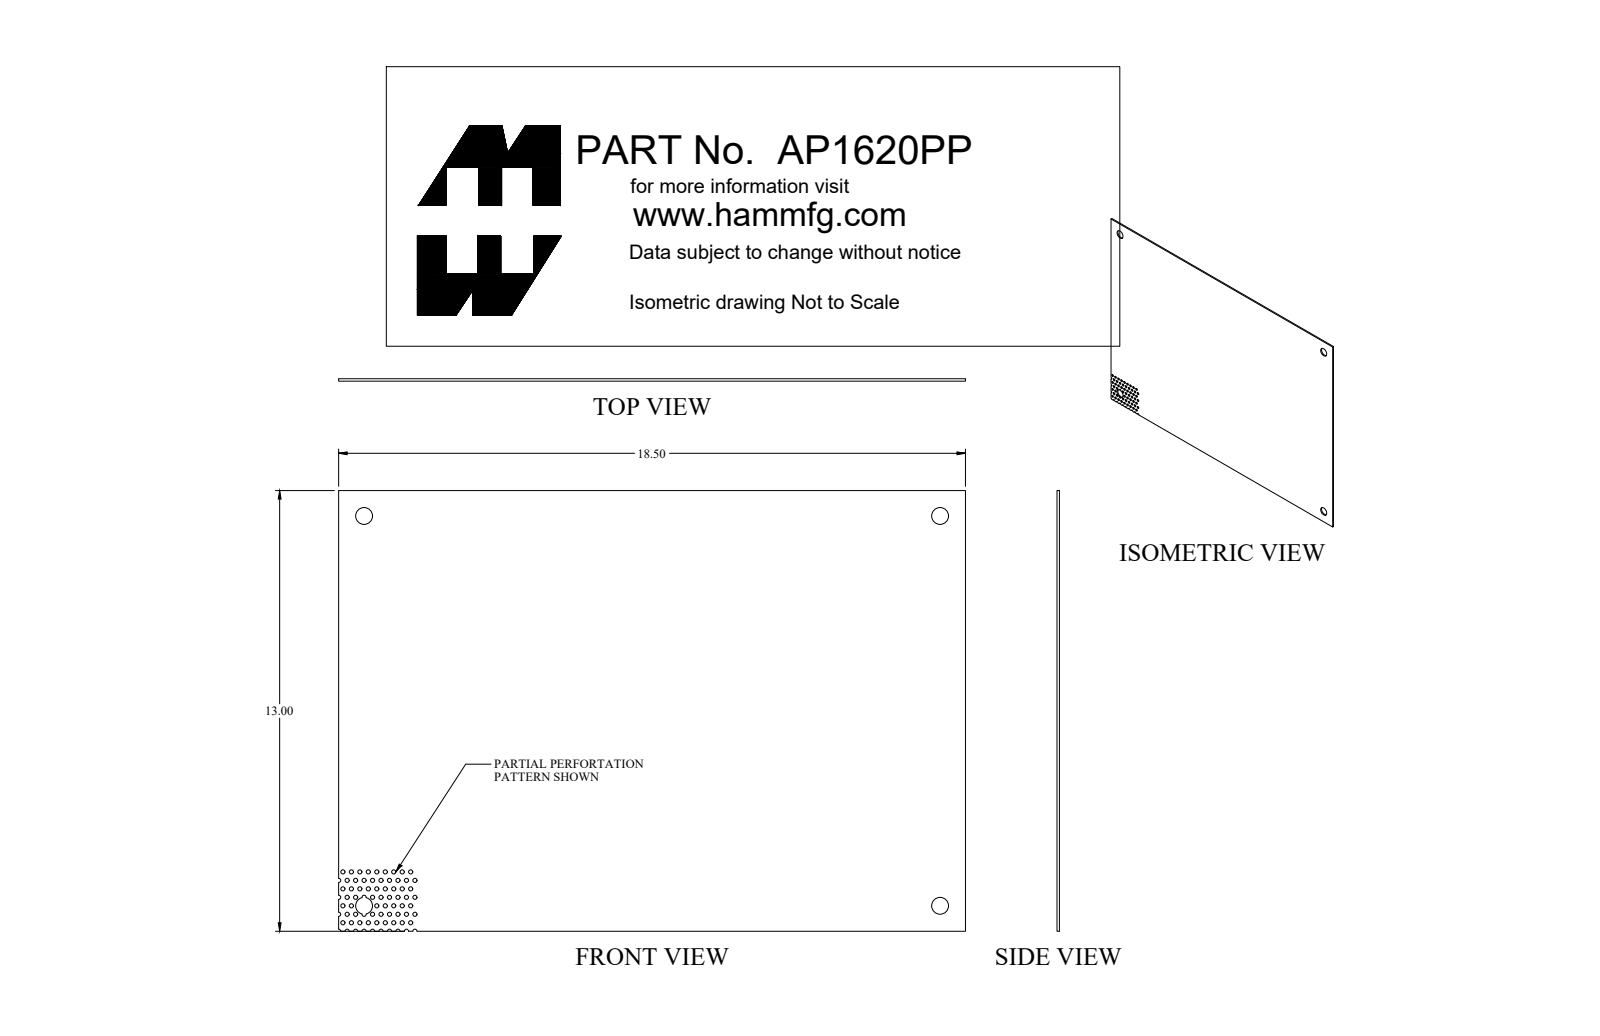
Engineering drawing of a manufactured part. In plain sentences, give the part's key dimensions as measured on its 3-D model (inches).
The part is named "AP1620PP_Default". Its 3-D file was written by "SolidWorks 2019 (CONFIG_CONTROL_DESIGN)". It is 1 solid with 169 faces: 18 planar, 151 cylindrical and 0 other. Overall it measures 18.5 by 13 by 0.072 inches. Its volume is 17.2 cubic inches and its surface area 484.5 square inches. Round holes: 50 of diameter 0.125, 9 of diameter 0.125, 4 of diameter 0.5. Partial cylindrical surfaces (rounded edges, fillets, slot ends): 15 of radius 0.062. The main face-to-face distances are 0.072, 13, 18.5. The hole center spacings are 0.28, 0.5, 0.25, 0.559, 0.451, 1.153, 0.673, 0.91.
